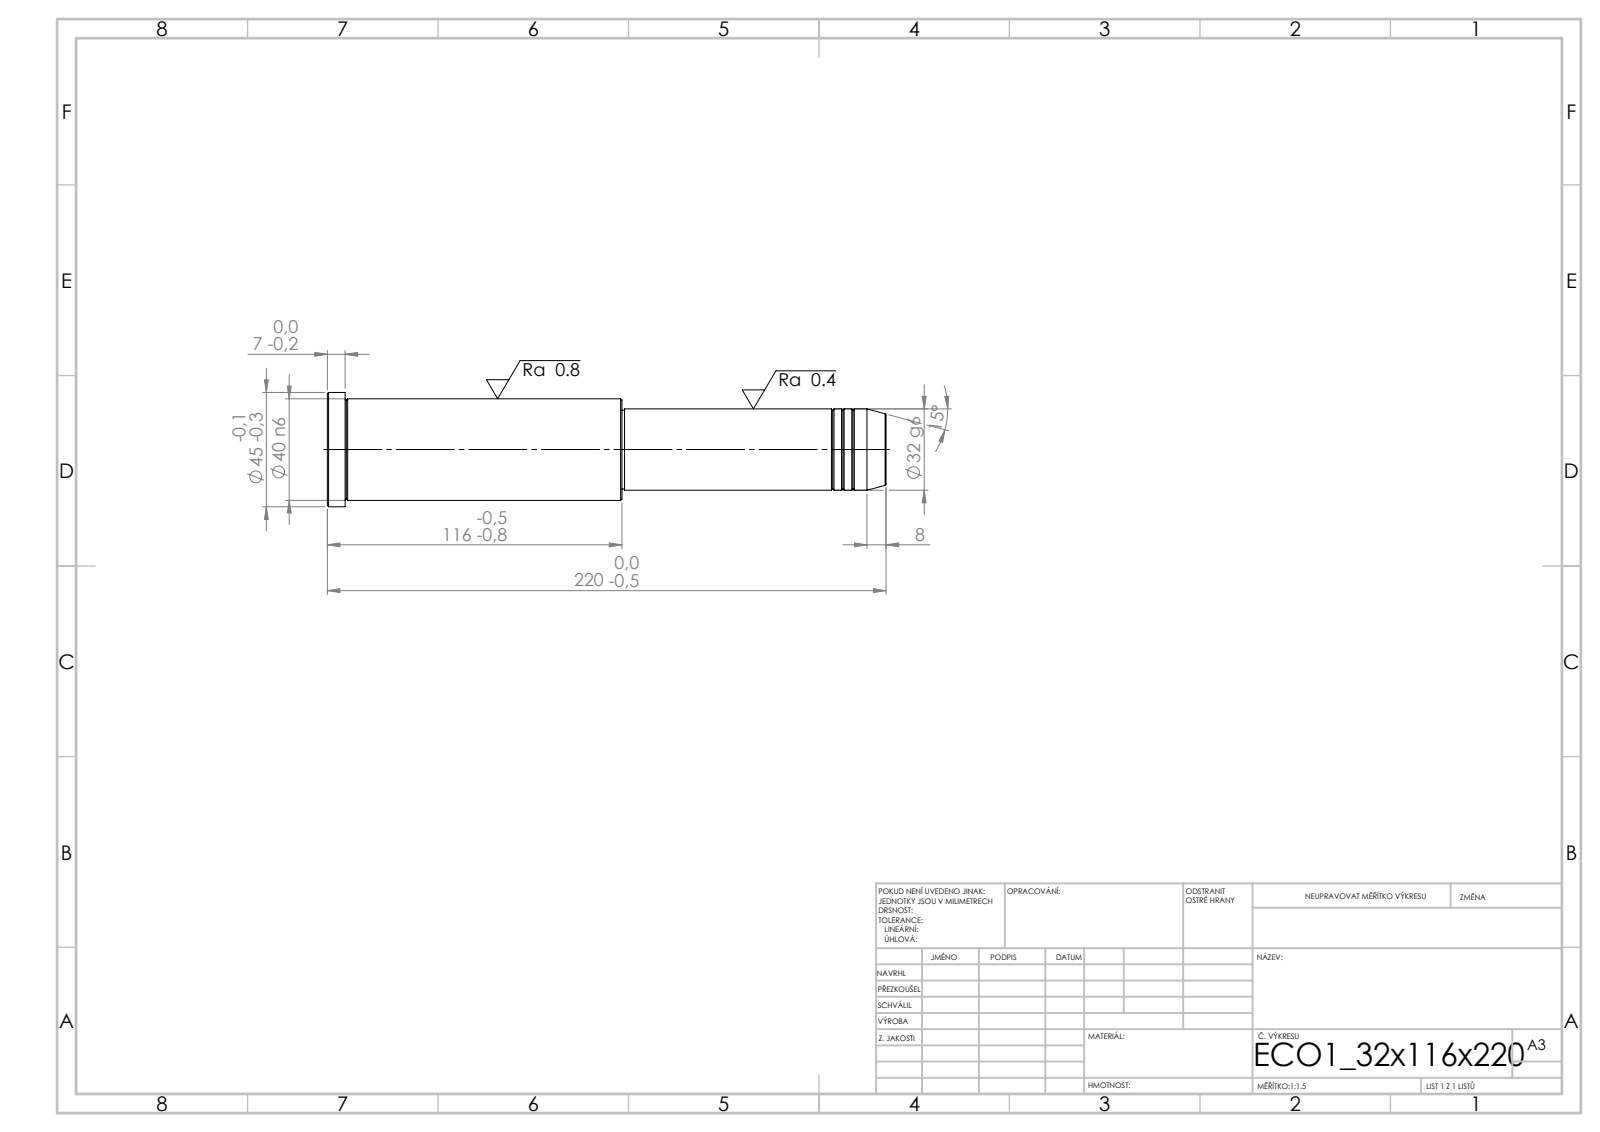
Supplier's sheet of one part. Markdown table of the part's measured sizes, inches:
| quantity | value |
| --- | --- |
| STEP written by | SolidWorks 2019 (CONFIG_CONTROL_DESIGN) |
| units | inches |
| bodies | 1 solid, 43 faces (5 planar, 14 cylindrical, 24 other) |
| overall size | 8.661 × 1.772 × 1.772 |
| volume | 14.08 in³ |
| surface area | 43.94 in² |
| round bosses / shafts (diameter × count) | 1.772 × 1, 1.575 × 1, 1.26 × 1, 1.22 × 1 |
| main face-to-face distances | 8.661, 4.094, 4.567, 8.386, 4.291, 0.276, 4.055, 0.039, 4.331, 4.606 |
